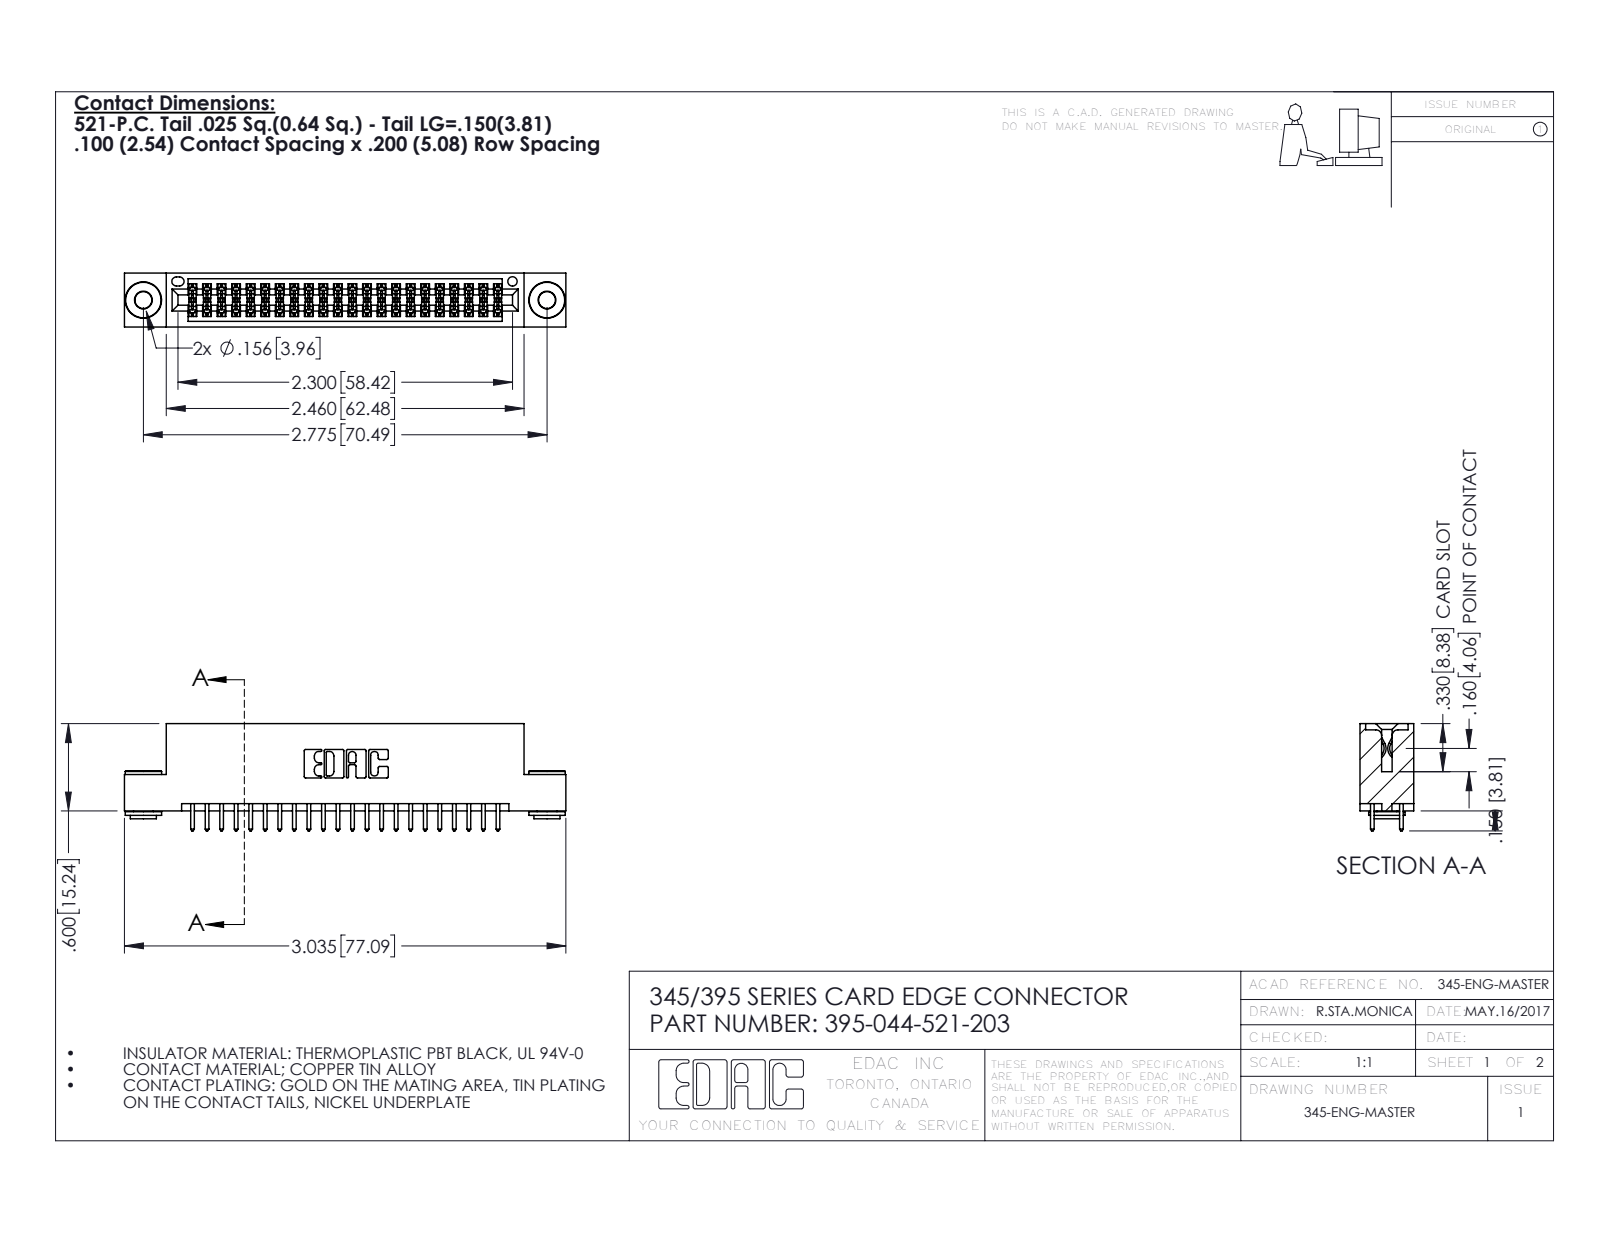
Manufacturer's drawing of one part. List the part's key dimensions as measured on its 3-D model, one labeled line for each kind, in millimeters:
Part name (STEP PRODUCT): 395-044-521-203; 345 Part_Flush Mounting Lugs - 0.156 Dia-TH; 345-250-002_345-250-002-102; 345-292-001_345-293-121
STEP written by: SolidWorks 2016 (CONFIG_CONTROL_DESIGN)
Units: millimetres
Bodies: 47 solids, 2364 faces (1542 planar, 814 cylindrical, 8 other)
Overall size (bounding box): 77.1 × 18.7 × 9.4
Volume: 7 310 mm³ · Surface area: 10 500 mm²
Round holes (diameter × count): ⌀2.9 ×2, ⌀4 ×2, ⌀1.6 ×1
Round bosses / shafts (diameter × count): ⌀6.4 ×2, ⌀4.6 ×2, ⌀3.5 ×2
Partial cylindrical surfaces — rounded edges, fillets, slot ends (radius × count): R0.2 ×66, R0.3 ×44, R0.3 ×22, R0.2 ×6, R0.8 ×6, R0.7 ×3, R0.4 ×2, R0.5 ×2
Main face-to-face distances: 1.8, 7.6, 5.1, 9.4, 0.6, 2.5, 6.9, 5.7, 4.4, 3.8
Hole centre spacings: 6.9, 64.5, 70.5
